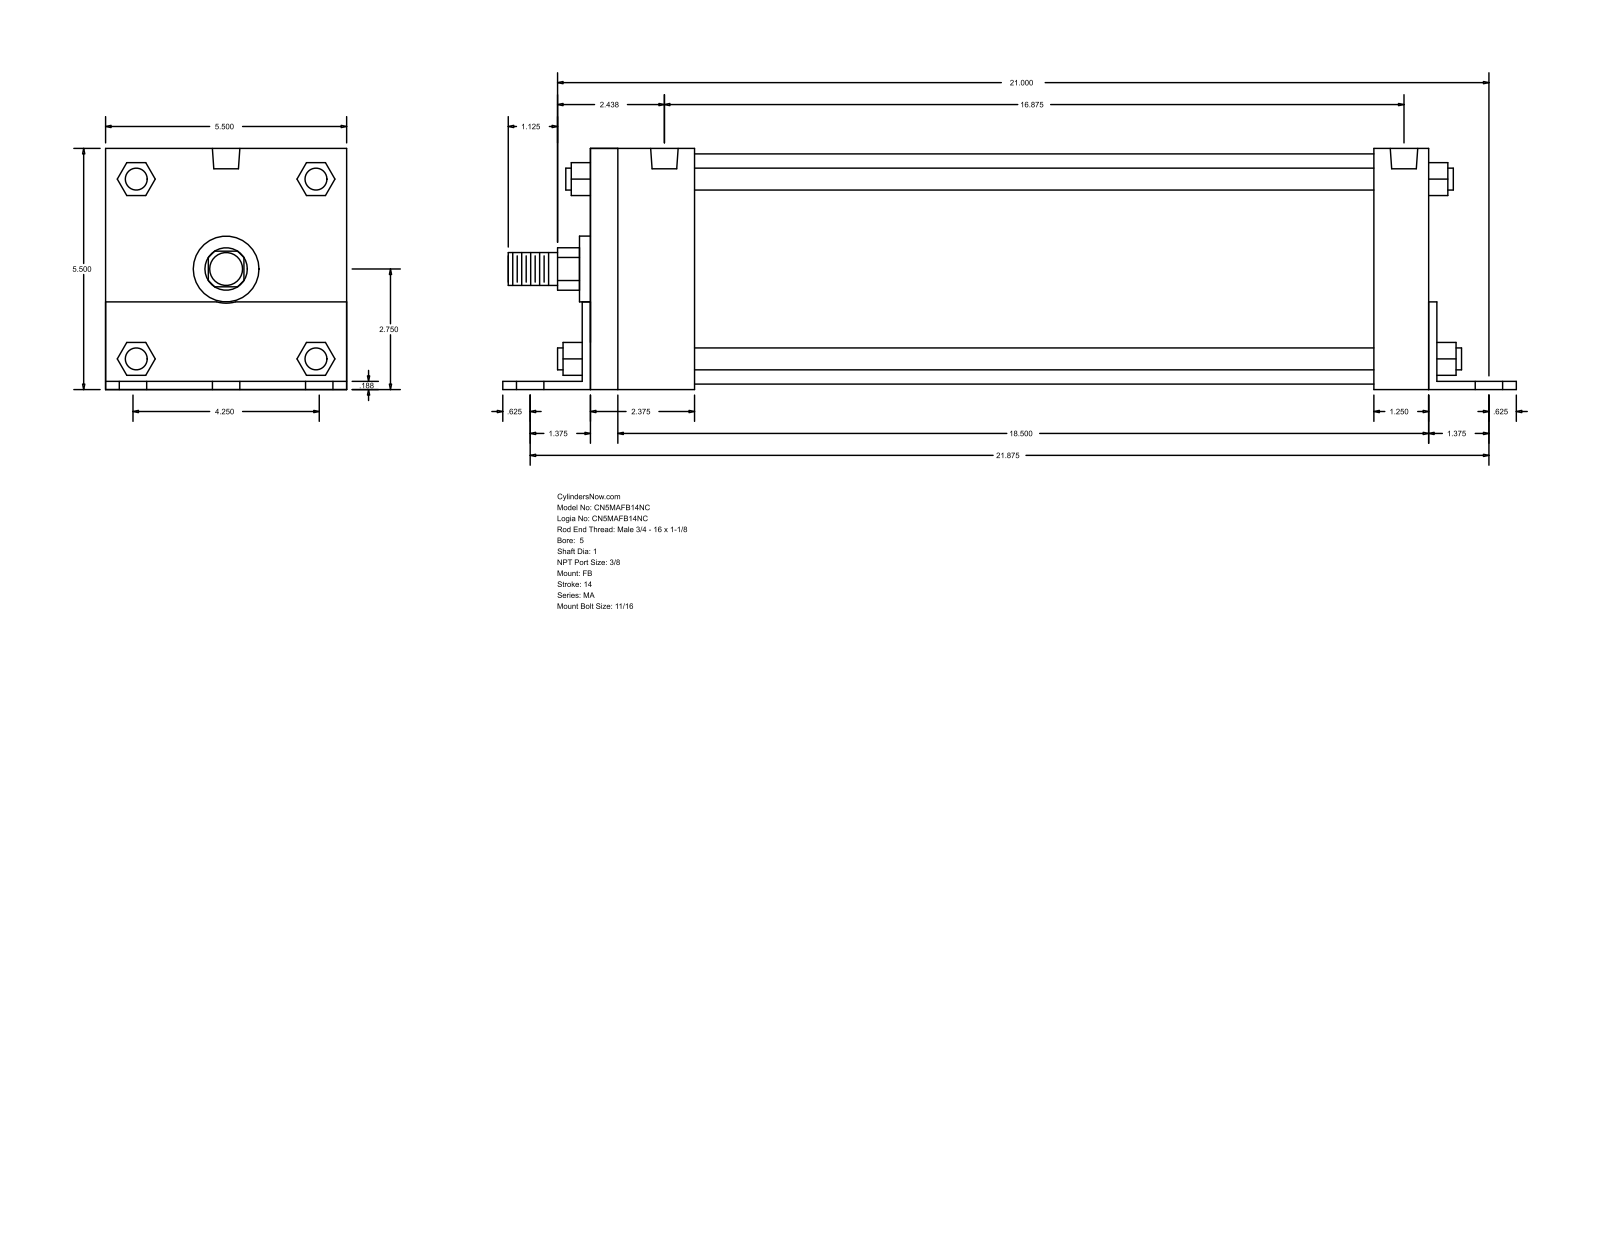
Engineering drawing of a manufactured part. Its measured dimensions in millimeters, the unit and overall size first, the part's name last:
Units: millimetres
Overall size (bounding box): 587.38 × 139.75 × 139.7
Round holes (diameter × count): ⌀17.46 ×6, ⌀11.11 ×4, ⌀15.93 ×2
Round bosses / shafts (diameter × count): ⌀12.7 ×4, ⌀133.35 ×1, ⌀38.1 ×1, ⌀25.4 ×1, ⌀19.05 ×1
Partial cylindrical surfaces — rounded edges, fillets, slot ends (radius × count): R12.29 ×1, R19.81 ×1
Main face-to-face distances: 139.7, 4.76, 139.75, 4.71, 134.99, 485.77, 4.77, 490.54, 490.53, 495.3
Hole centre spacings: 53.98, 558.25, 555.63, 73.04, 76.34, 94.68, 98.63, 107.96
Bodies: 0 solids, 140 faces (105 planar, 35 cylindrical, 0 other)
Part name (STEP PRODUCT): MA_FB__0500_1
STEP written by: GSSL Pune (CONFIG_CONTROL_DESIGN)
